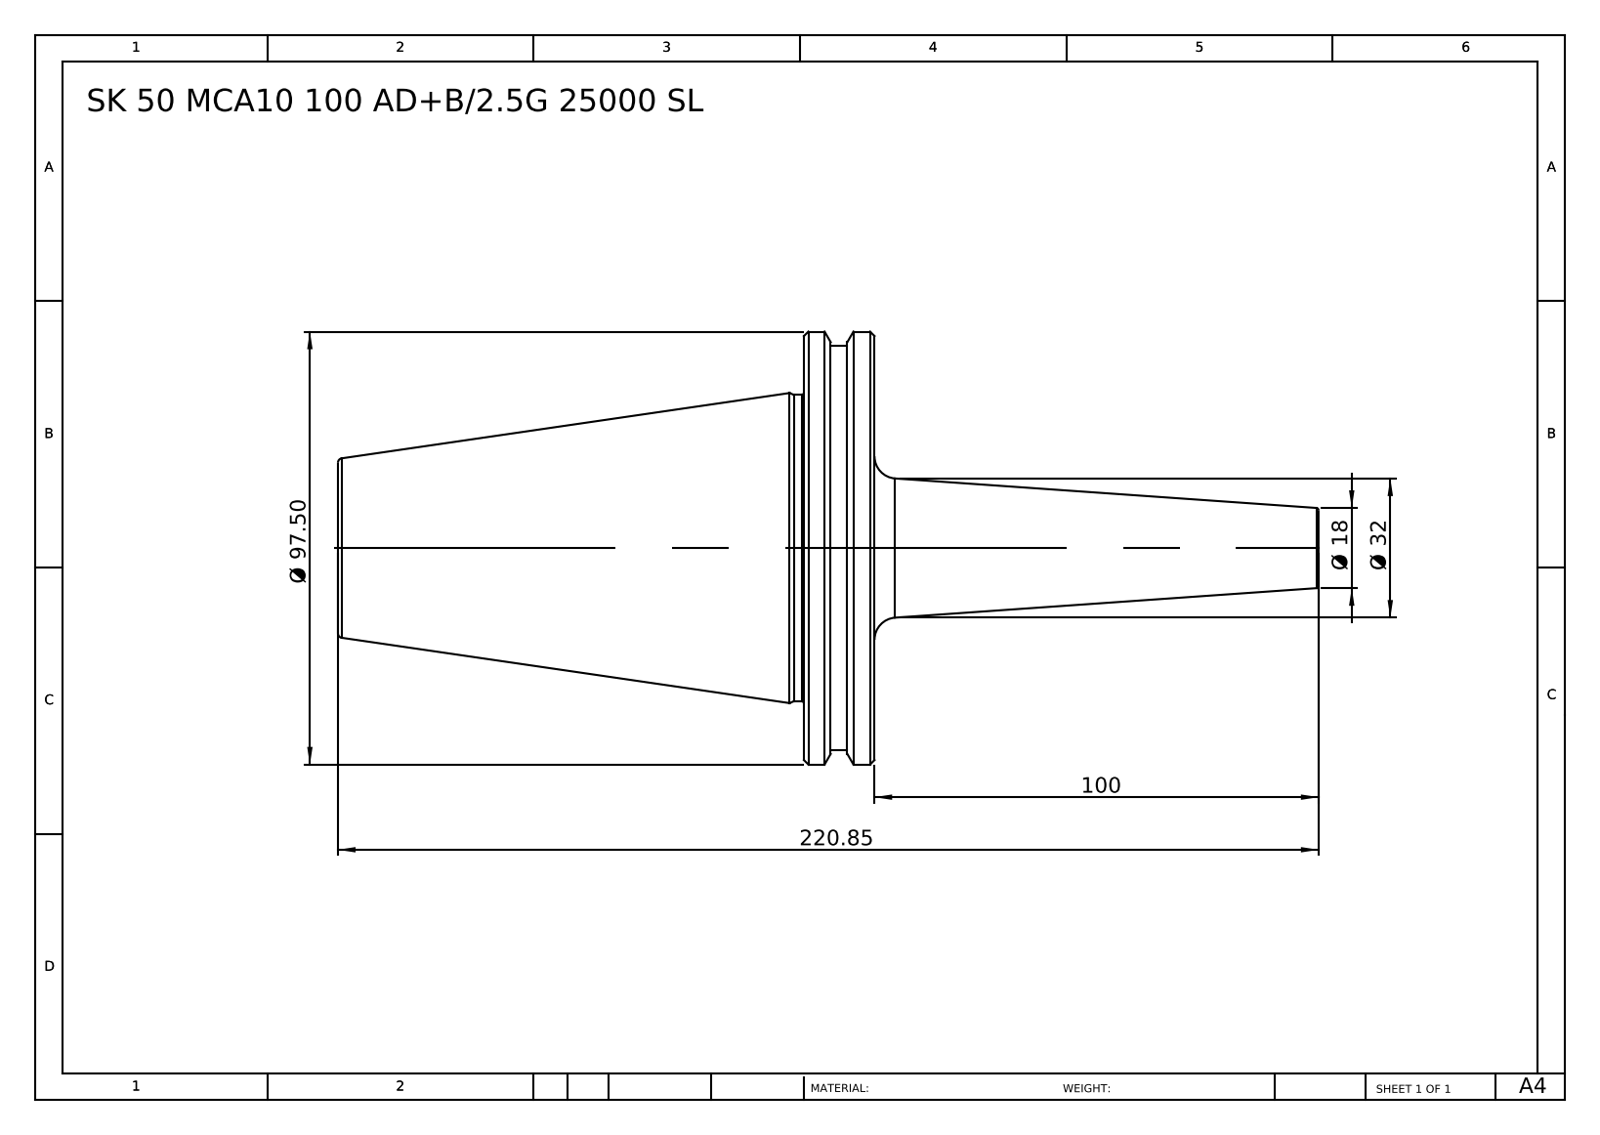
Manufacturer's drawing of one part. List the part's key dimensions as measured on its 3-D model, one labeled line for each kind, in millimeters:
Part name (STEP PRODUCT): SK 50 MCA10 100 AD+B-2.5G25000 SL
STEP written by: SolidWorks 2014 (CONFIG_CONTROL_DESIGN)
Units: millimetres
Bodies: 1 solid, 36 faces (6 planar, 8 cylindrical, 22 other)
Overall size (bounding box): 220.85 × 97.5 × 97.5
Volume: 424 391 mm³ · Surface area: 43 741 mm²
Round bosses / shafts (diameter × count): ⌀97.5 ×1, ⌀91 ×1, ⌀69 ×1
Main face-to-face distances: 15.9, 120.85, 104.95, 6.13, 9.77, 114.72, 9.88, 3.75, 6.02, 110.97
